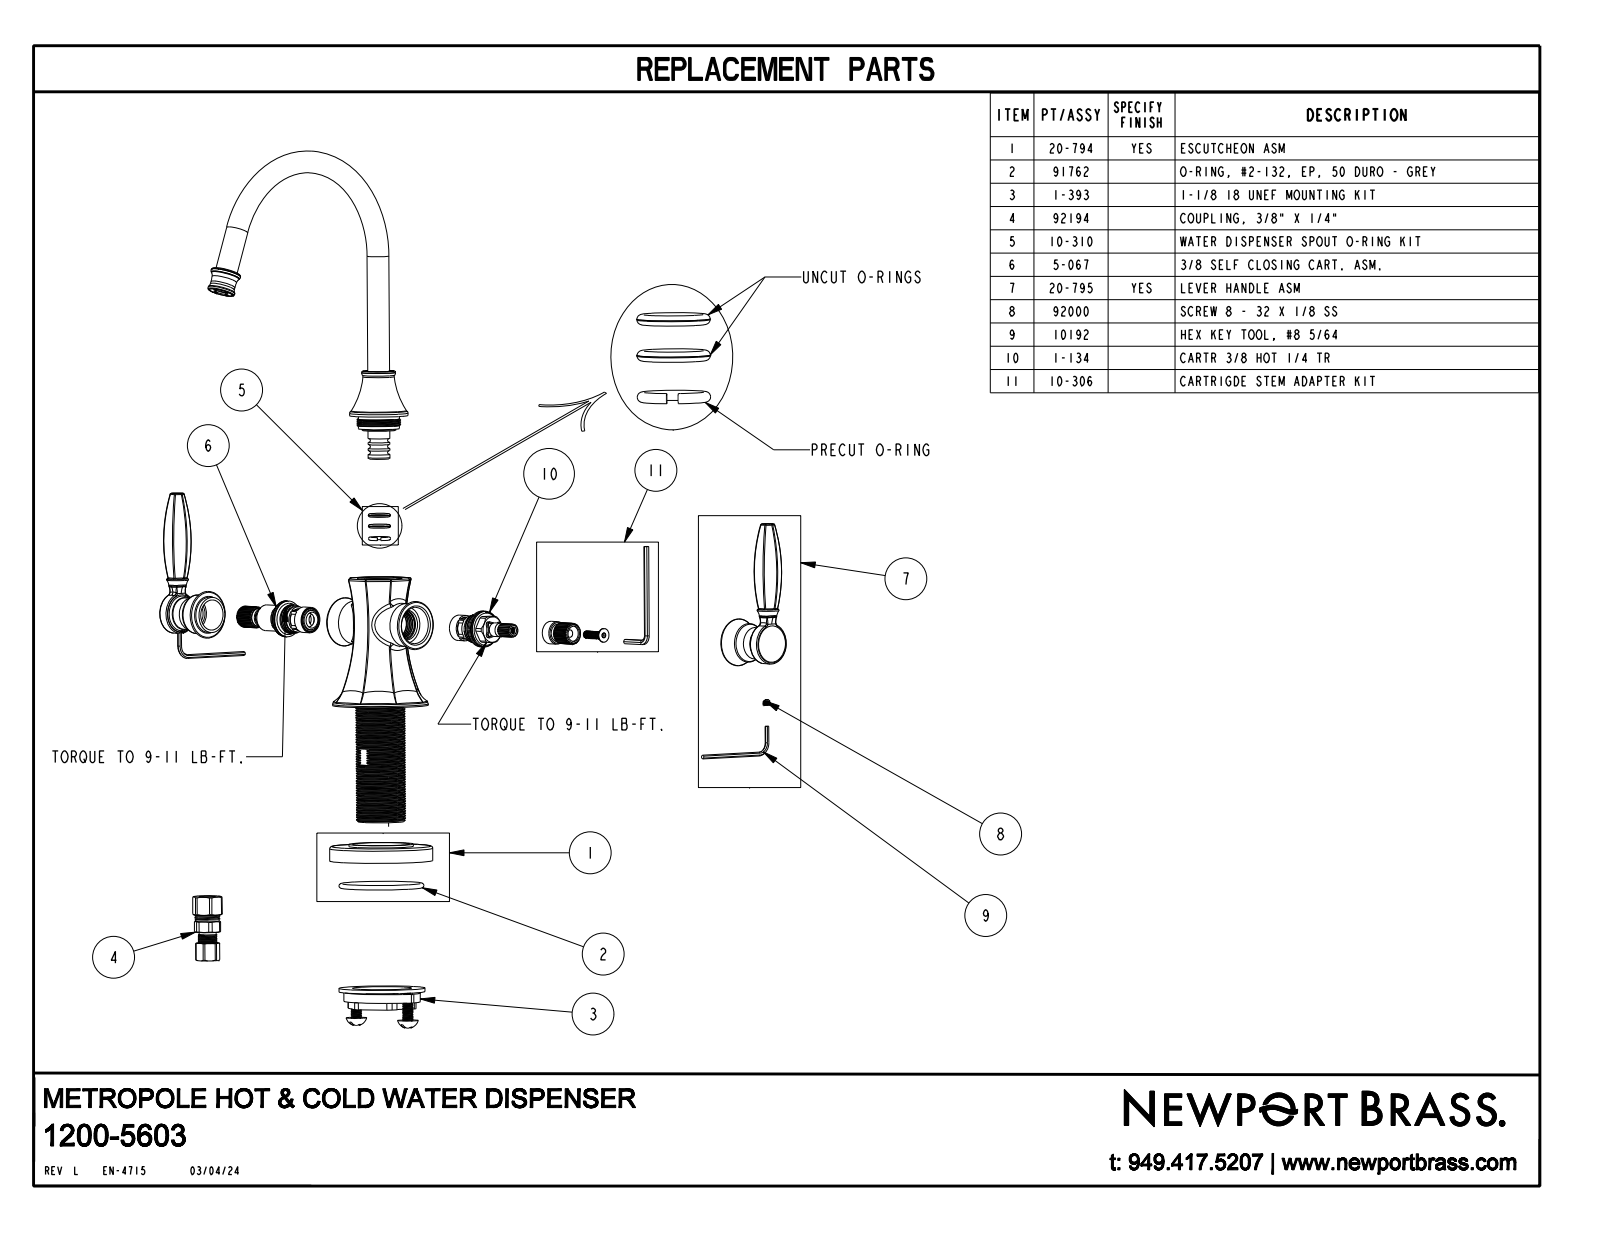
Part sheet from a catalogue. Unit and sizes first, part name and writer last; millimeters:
Units: millimetres
Overall size (bounding box): 256.3 × 157.8 × 132.4
Round bosses / shafts (diameter × count): ⌀12.7 ×2, ⌀59.9 ×1, ⌀55.9 ×1, ⌀34 ×1, ⌀24.9 ×1, ⌀23.3 ×1, ⌀18.3 ×1
Main face-to-face distances: 0.5, 62.5, 62, 63, 8.4, 108.2, 99.8, 29.5, 30, 92
Volume: 204 500 mm³ · Surface area: 40 310 mm²
Bodies: 1 solid, 468 faces (28 planar, 20 cylindrical, 420 other)
Part name (STEP PRODUCT): 1200-5603
STEP written by: CREO PARAMETRIC BY PTC INC, 2018400 (CONFIG_CONTROL_DESIGN)
